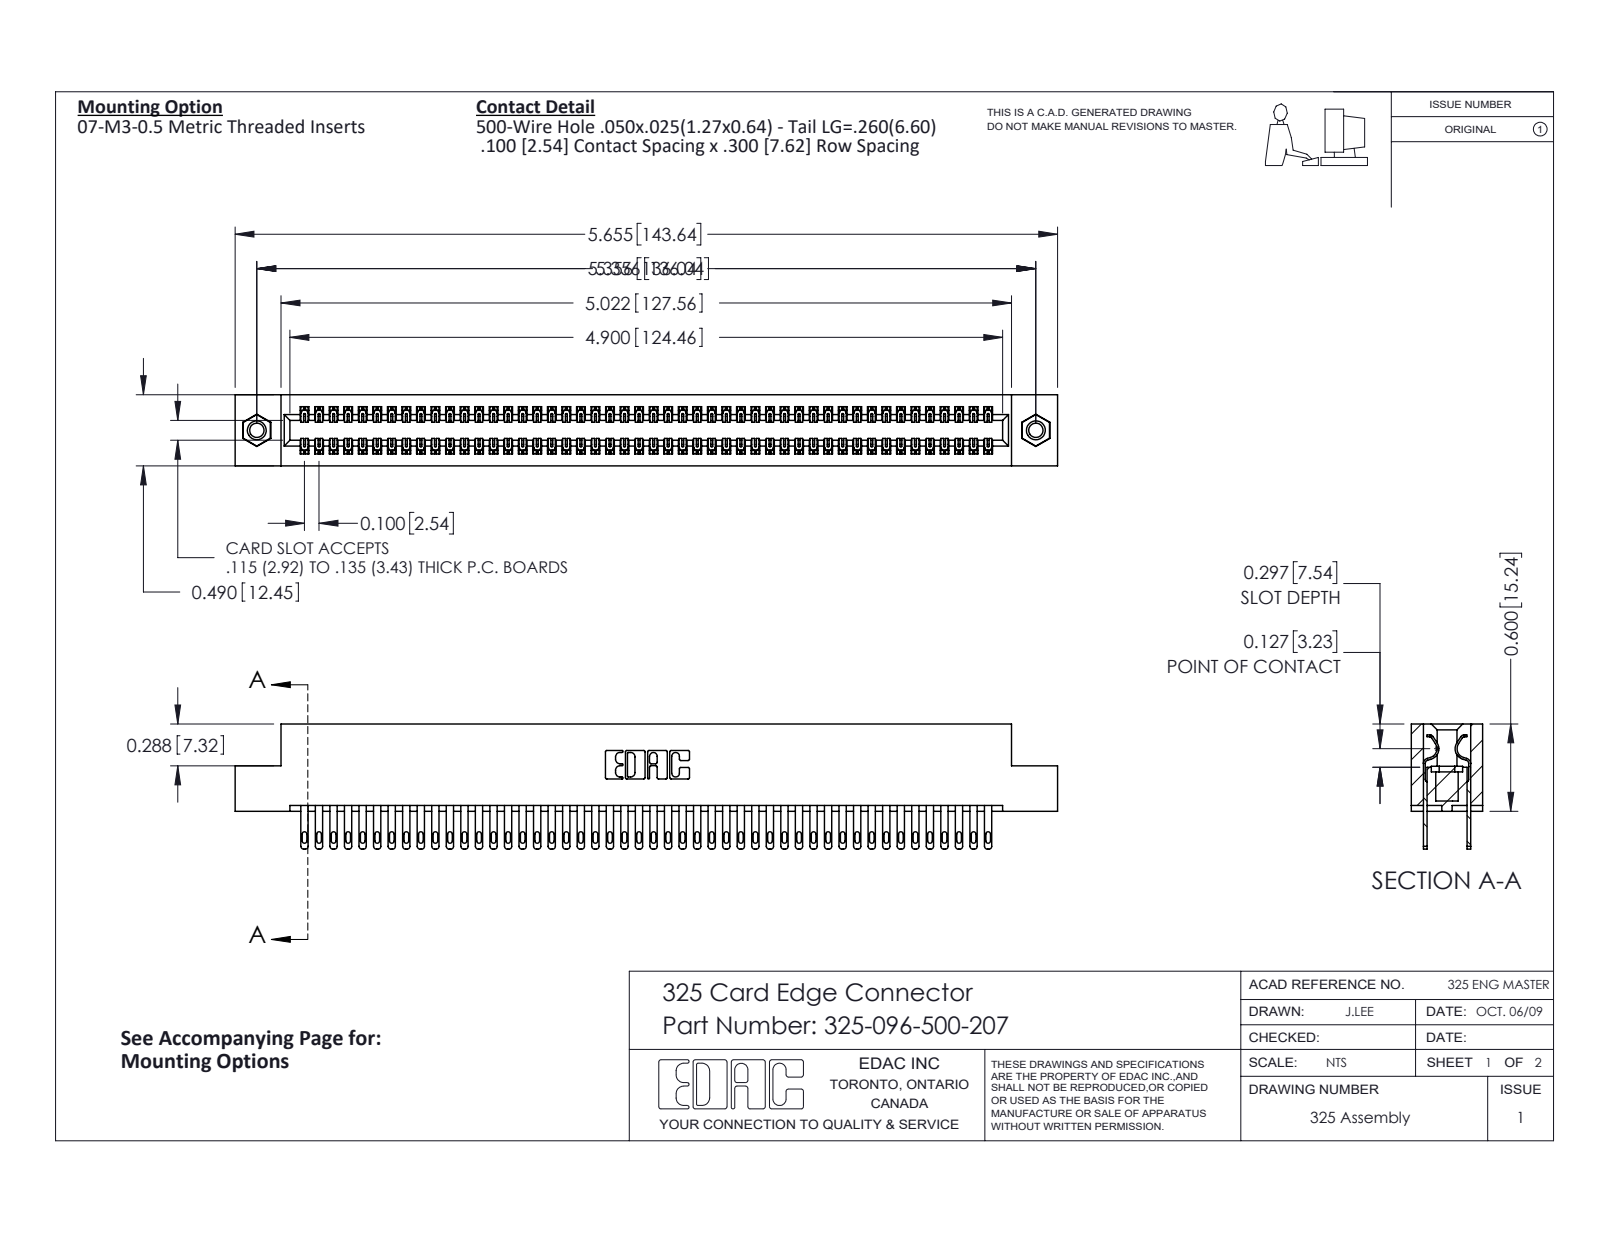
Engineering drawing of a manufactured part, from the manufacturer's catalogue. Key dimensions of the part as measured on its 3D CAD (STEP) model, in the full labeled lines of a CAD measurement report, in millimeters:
Part name (STEP PRODUCT): 345-250-001_345-250-005-103; 325-292-001_325-293-100; 325-096-500-207; 325 Part_TI
STEP written by: SolidWorks 2016 (CONFIG_CONTROL_DESIGN)
Units: millimetres
Bodies: 99 solids, 4782 faces (2982 planar, 1784 cylindrical, 16 other)
Overall size (bounding box): 143.6 × 21.8 × 12.4
Volume: 18 880 mm³ · Surface area: 24 020 mm²
Round holes (diameter × count): ⌀2.5 ×2, ⌀3.2 ×2, ⌀4.1 ×2
Round bosses / shafts (diameter × count): ⌀3.9 ×2
Partial cylindrical surfaces — rounded edges, fillets, slot ends (radius × count): R0.2 ×144, R0.4 ×96, R0.5 ×96, R0.3 ×22, R0.2 ×6, R0.8 ×6, R0.7 ×3, R0.4 ×2
Main face-to-face distances: 2.1, 10.3, 7.6, 2.7, 9.7, 0.6, 12.4, 8.3, 7, 14.2
Hole centre spacings: 136
